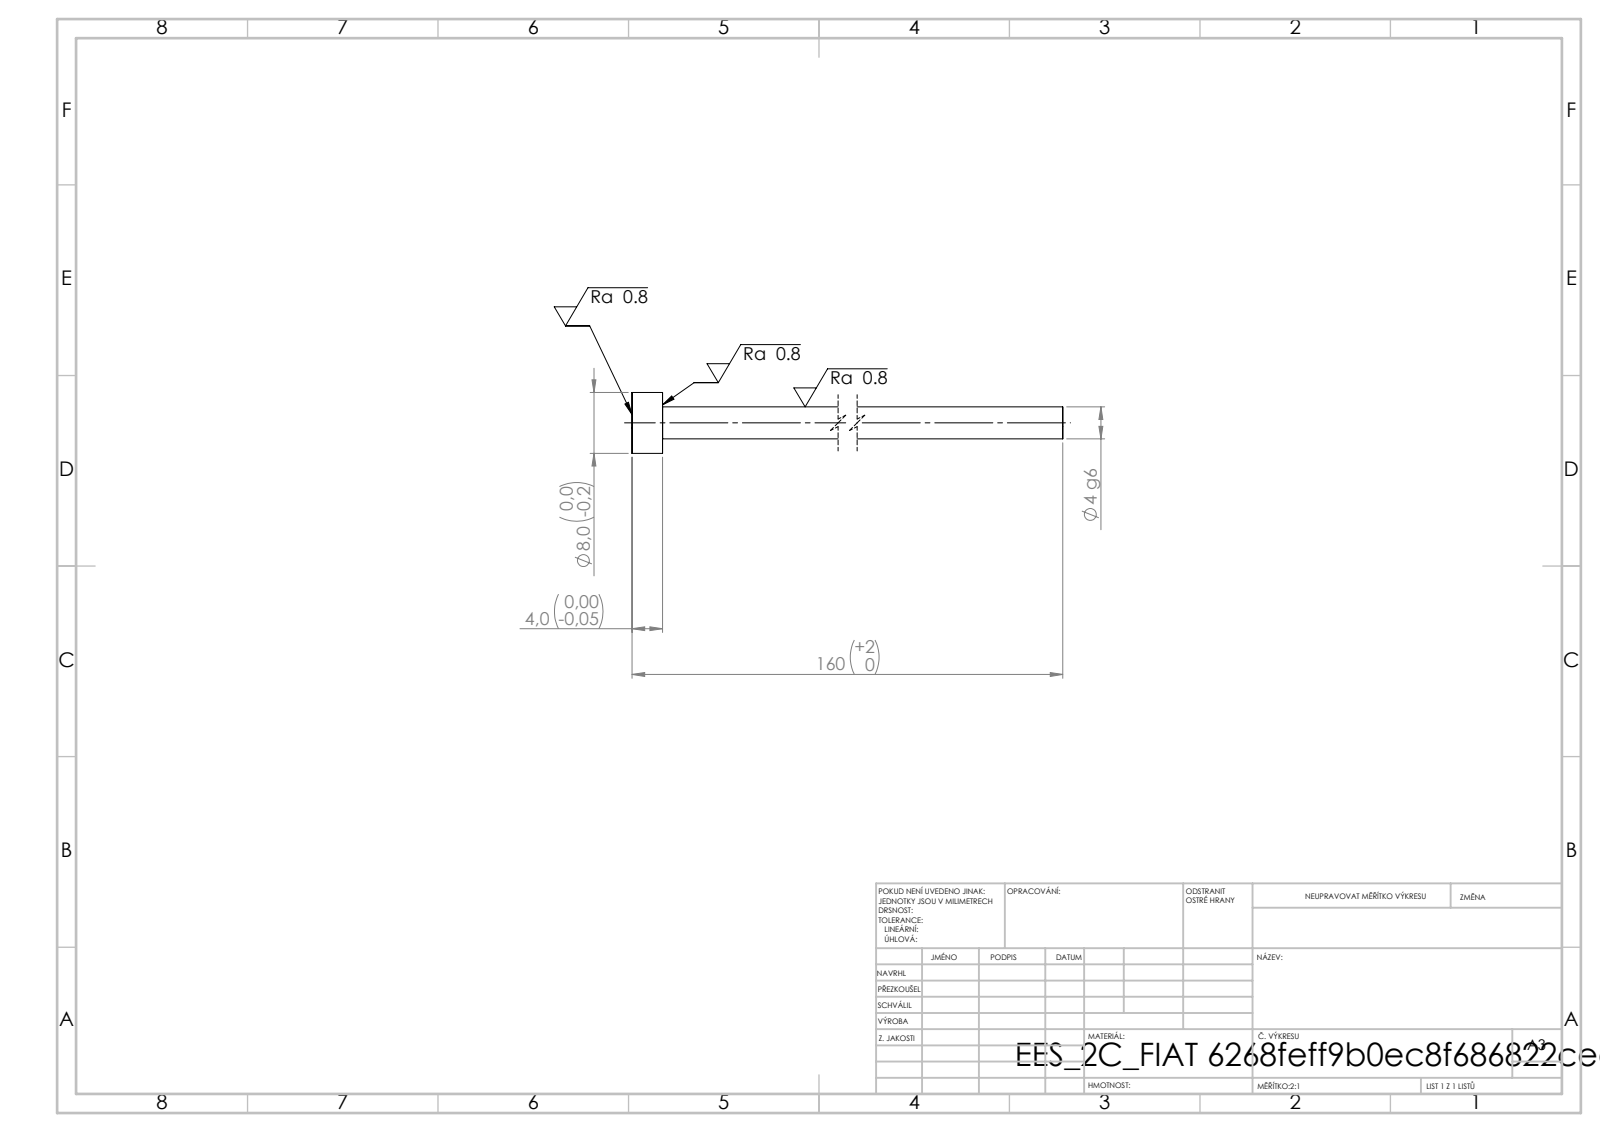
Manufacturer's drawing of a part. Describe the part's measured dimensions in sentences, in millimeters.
Its 3-D file was written by "SolidWorks 2019 (CONFIG_CONTROL_DESIGN)". It is 1 solid with 7 faces: 3 planar, 4 cylindrical and 0 other. Overall it measures 160 by 8 by 8 millimeters. Its volume is 2 362 cubic millimeters and its surface area 2 259 square millimeters. Round bosses or shafts: 1 of diameter 8, 1 of diameter 4.2. The main face-to-face distances are 4, 160, 156.
